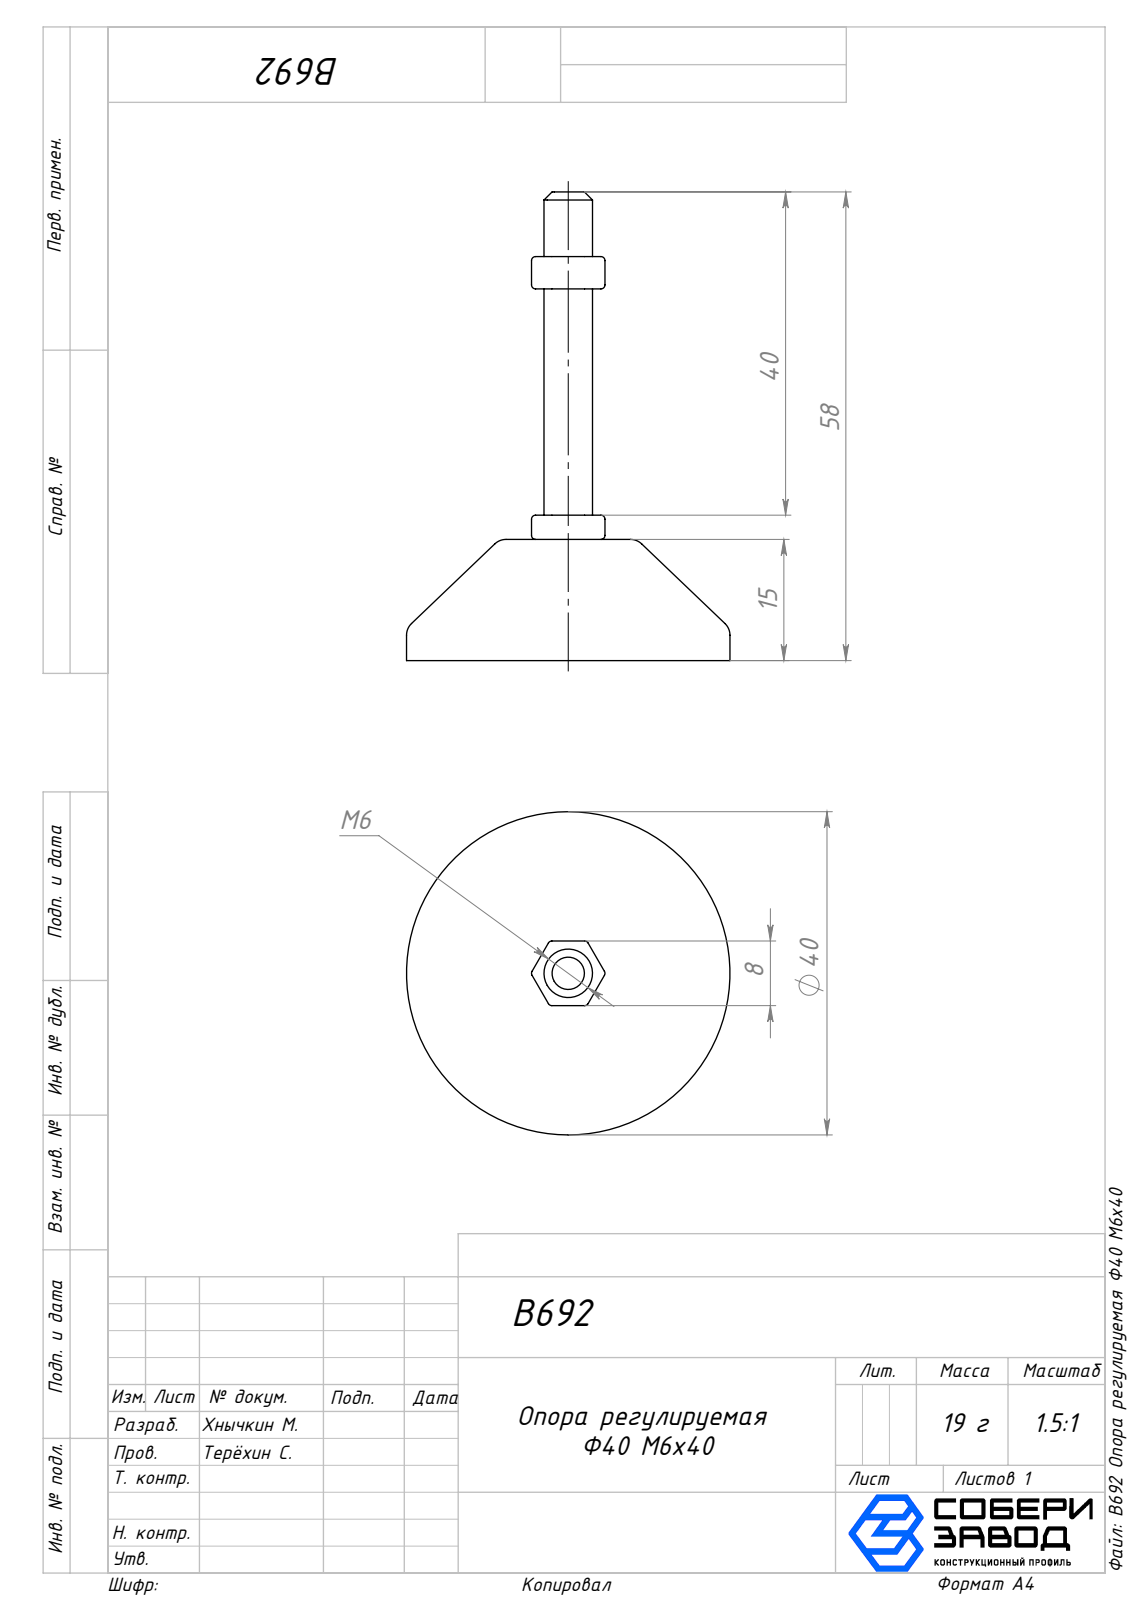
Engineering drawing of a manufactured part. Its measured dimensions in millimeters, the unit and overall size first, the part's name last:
Units: millimetres
Overall size (bounding box): 58 × 40 × 40
Round holes (diameter × count): ⌀4 ×1, ⌀32 ×1
Round bosses / shafts (diameter × count): ⌀40 ×1, ⌀6 ×1, ⌀5 ×1
Partial cylindrical surfaces — rounded edges, fillets, slot ends (radius × count): R0.5 ×42
Main face-to-face distances: 4, 15, 11, 8, 46, 50, 35, 42, 31, 18
Volume: 10 957 mm³ · Surface area: 5 511 mm²
Bodies: 4 solids, 153 faces (29 planar, 68 cylindrical, 56 other)
Part name (STEP PRODUCT): Опора_00; Вал_00; Гайка_00; B692 Опора регулируемая Ф40 M6х40 (+1 more)
STEP written by: SolidWorks 2025 (AUTOMOTIVE_DESIGN)
